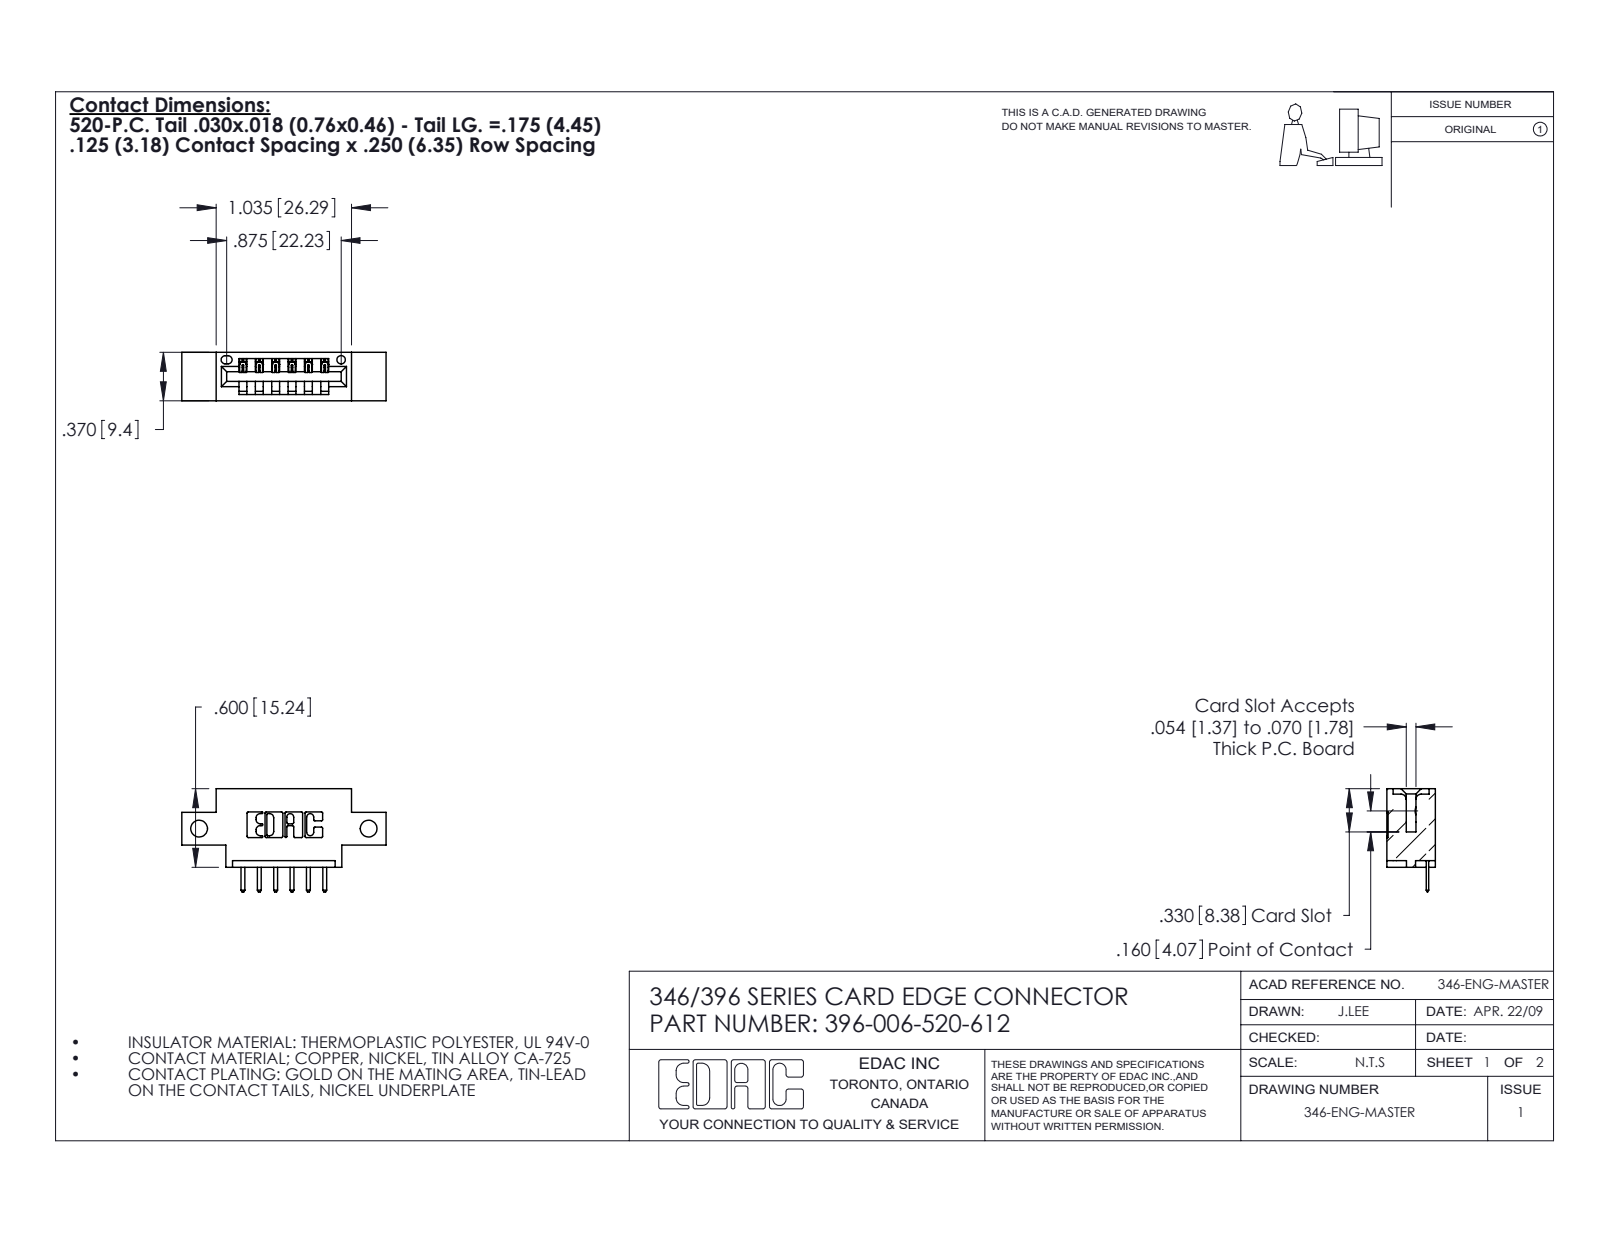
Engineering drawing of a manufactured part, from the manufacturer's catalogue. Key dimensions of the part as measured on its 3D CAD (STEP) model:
Part name (STEP PRODUCT): 396-006-520-612; 345-292-001_345-293-120; 346 Part_0.170 Offset - Side Mount
STEP written by: SolidWorks 2020 (CONFIG_CONTROL_DESIGN)
Units: inches
Bodies: 7 solids, 498 faces (332 planar, 166 cylindrical, 0 other)
Overall size (bounding box): 1.56 × 0.788 × 0.37
Volume: 0.201 in³ · Surface area: 5.697 in²
Round holes (diameter × count): ⌀0.128 ×2, ⌀0.064 ×1
Partial cylindrical surfaces — rounded edges, fillets, slot ends (radius × count): R0.01 ×22, R0.01 ×14, R0.006 ×12, R0.007 ×6, R0.031 ×6, R0.026 ×3, R0.031 ×2, R0.04 ×2
Main face-to-face distances: 0.25, 0.37, 0.048, 0.322, 0.148, 0.222, 0.1, 0.174, 0.125, 0.185
Hole centre spacings: 1.295
